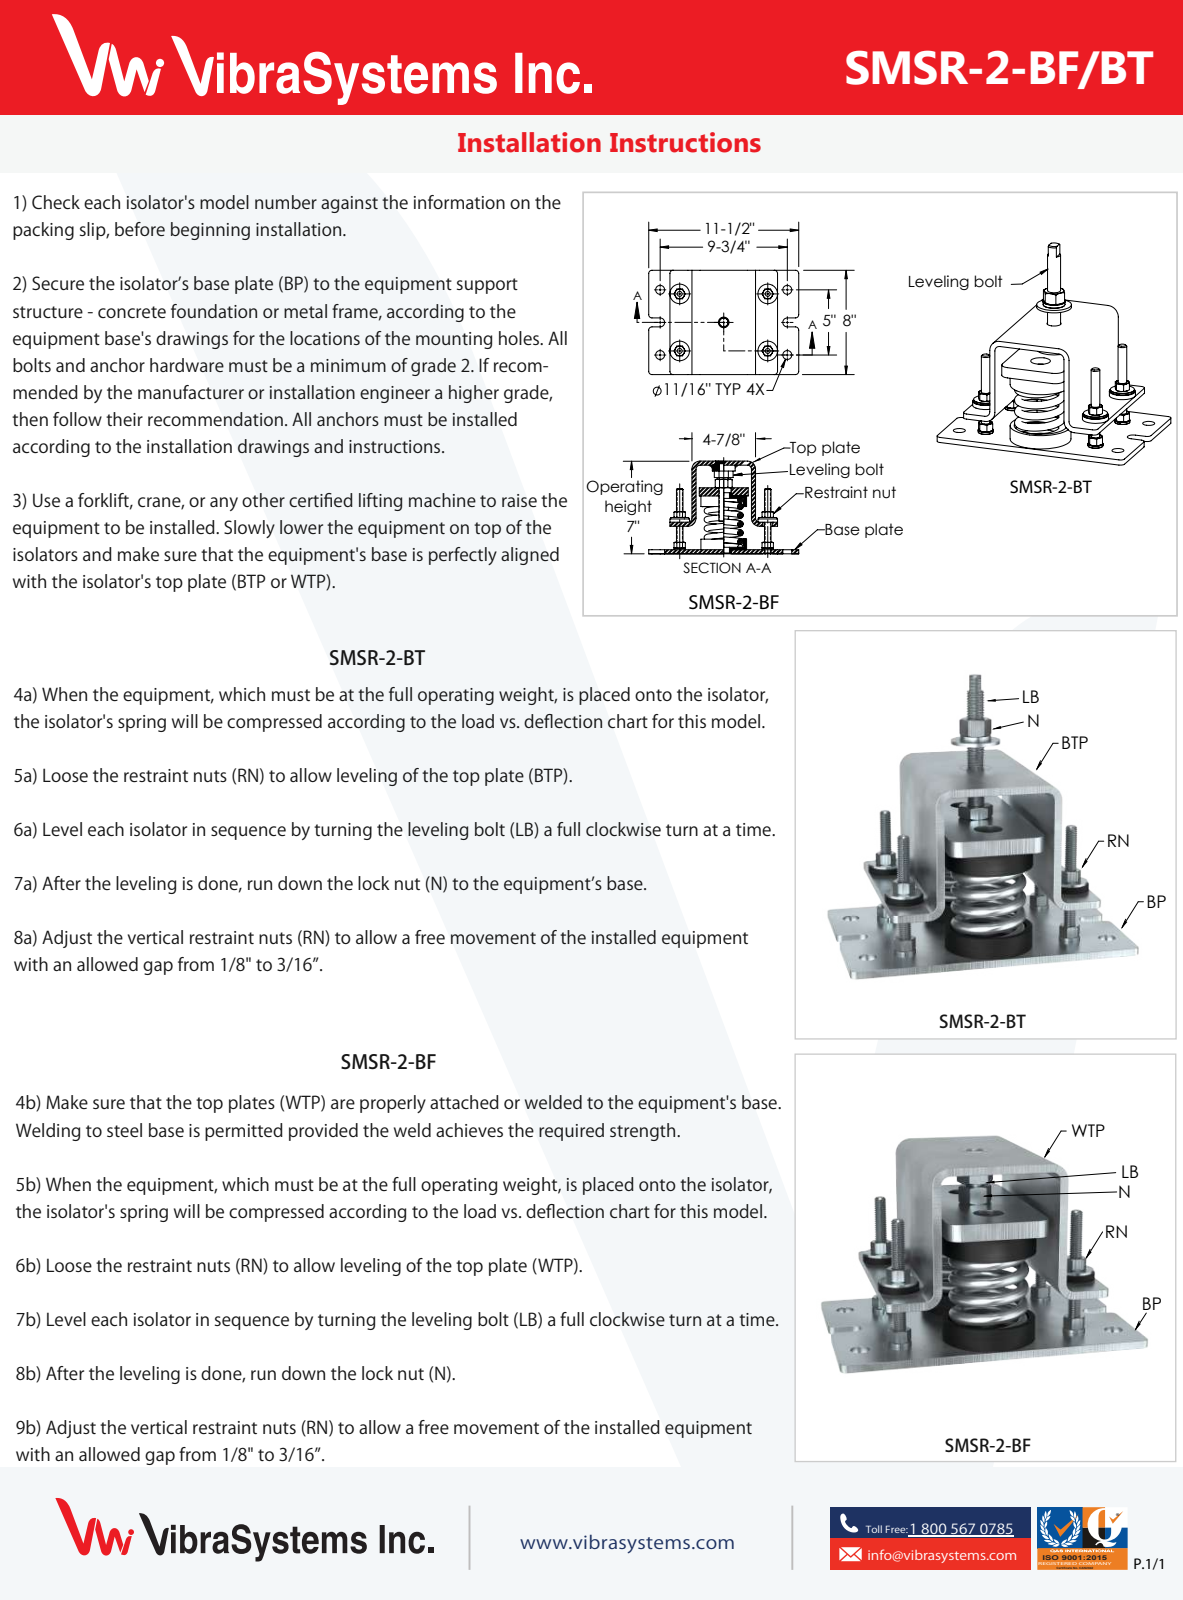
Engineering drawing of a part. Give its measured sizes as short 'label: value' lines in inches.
name: SMSR-2-BF Rev B
written by: SolidWorks 2016 (CONFIG_CONTROL_DESIGN)
unit: in
bodies: 1 solid, 280 faces (172 planar, 92 cylindrical, 16 other)
size: 11.5 × 8 × 7
volume: 167.6 in³; area: 658.3 in²
holes: 4× ⌀0.687, 1× ⌀0.75
bosses: 4× ⌀1.5, 4× ⌀1.4, 4× ⌀0.82, 4× ⌀0.5, 2× ⌀3.5, 2× ⌀3, 1× ⌀1.75
rounds: 14× R0.25, 6× R0.5, 2× R0.344, 2× R0.562, 1× R0.187, 1× R0.188
face distances: 0.313, 4.562, 6.687, 1.687, 2, 5, 4.687, 4.875, 4.25, 7
hole spacings: 5.478, 5, 9.75, 10.957
